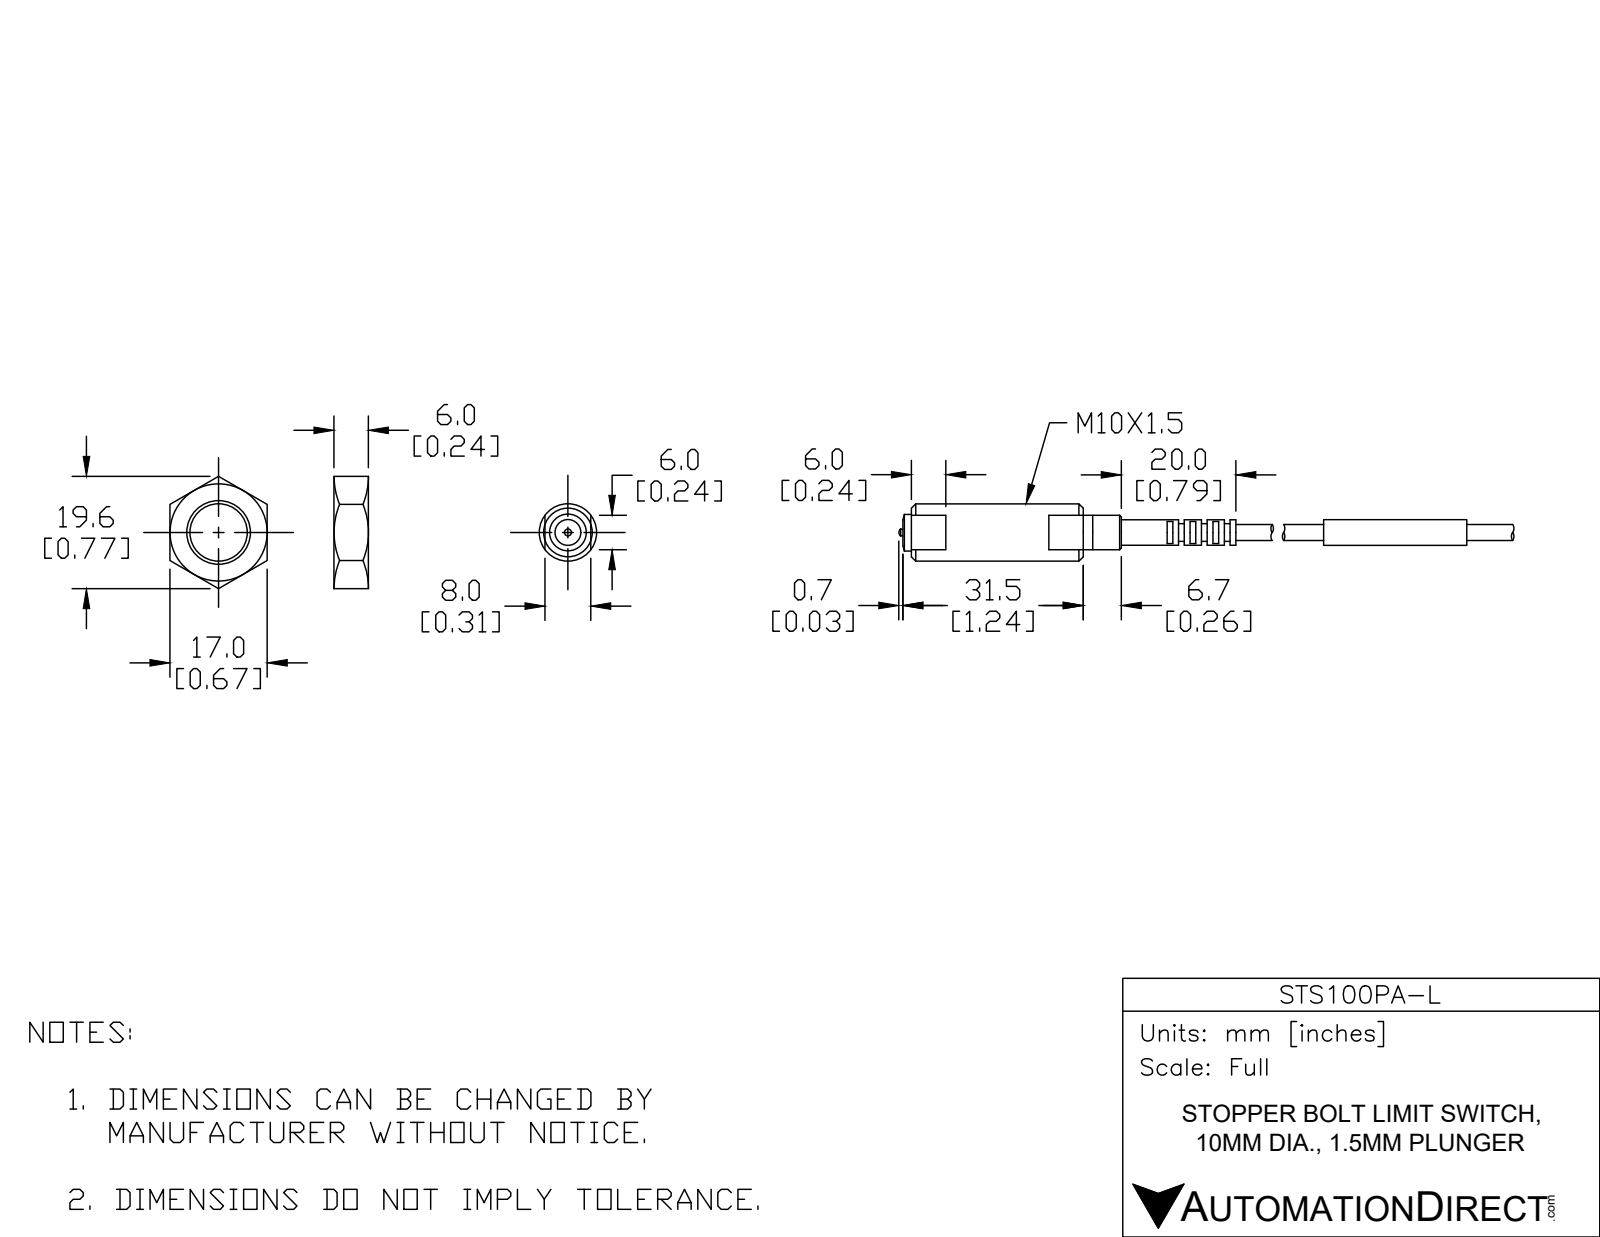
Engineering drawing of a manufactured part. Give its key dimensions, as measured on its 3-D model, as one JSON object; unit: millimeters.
{"part_name": "STS100PA-L", "step_written_by": "SolidWorks 2017 (CONFIG_CONTROL_DESIGN)", "units": "millimeters", "bodies": {"solids": 2, "faces": 211, "planar": 66, "cylindrical": 78, "other": 67}, "overall_size": [109.85, 10, 10], "volume_mm3": 2952, "surface_area_mm2": 2539, "round_bosses_or_shafts": [[10, 1], [6.3, 1], [6, 1], [4.5, 1], [4.45, 1], [3.1, 1], [2.8, 1], [1.2, 1]], "face_to_face_distances": [1, 8, 2, 3, 4, 5, 6, 7, 30, 9]}
